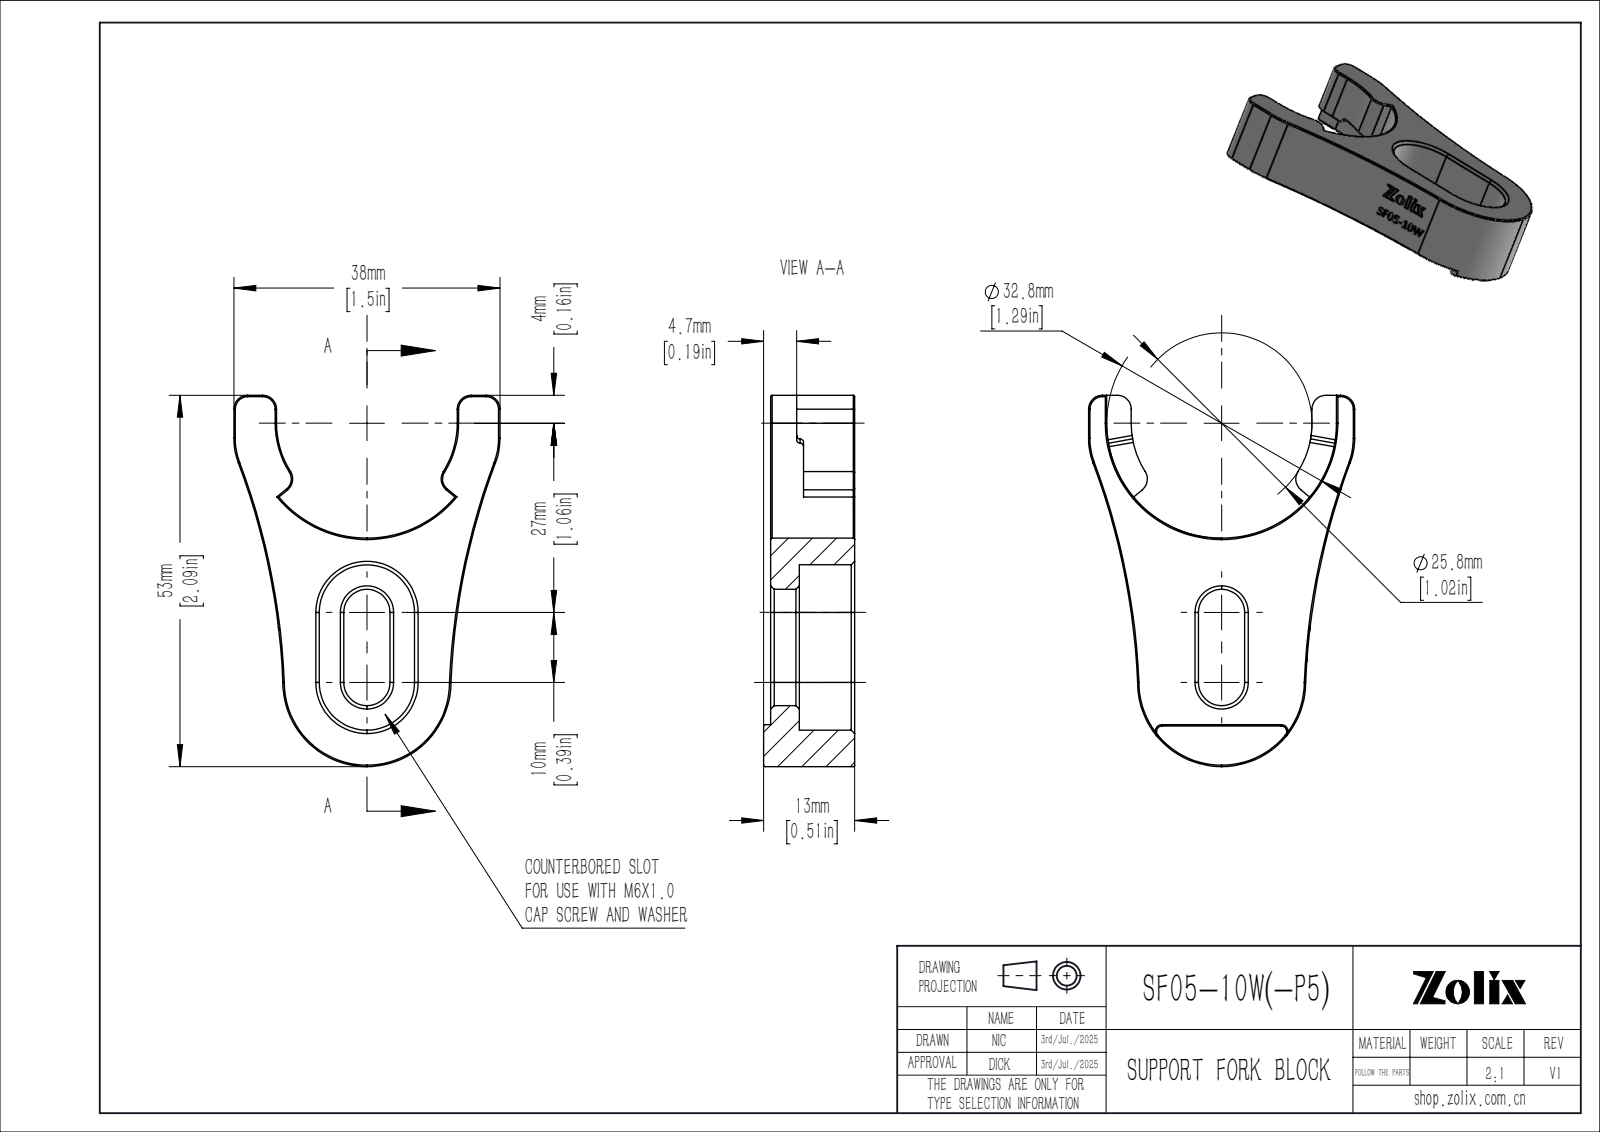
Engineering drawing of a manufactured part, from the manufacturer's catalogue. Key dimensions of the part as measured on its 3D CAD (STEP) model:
Part name (STEP PRODUCT): SF05-10W
STEP written by: SolidWorks 2020 (CONFIG_CONTROL_DESIGN)
Units: millimetres
Bodies: 1 solid, 386 faces (66 planar, 63 cylindrical, 257 other)
Overall size (bounding box): 53 × 38 × 13
Volume: 9 382 mm³ · Surface area: 4 756 mm²
Partial cylindrical surfaces — rounded edges, fillets, slot ends (radius × count): R0.2 ×13, R2 ×6, R0.5 ×4, R1 ×2, R3.3 ×2, R6.8 ×2, R10 ×2, R101 ×2
Main face-to-face distances: 12, 4.1, 7.9, 1, 25.8, 12.2, 3.5, 4.7, 5.1, 13
